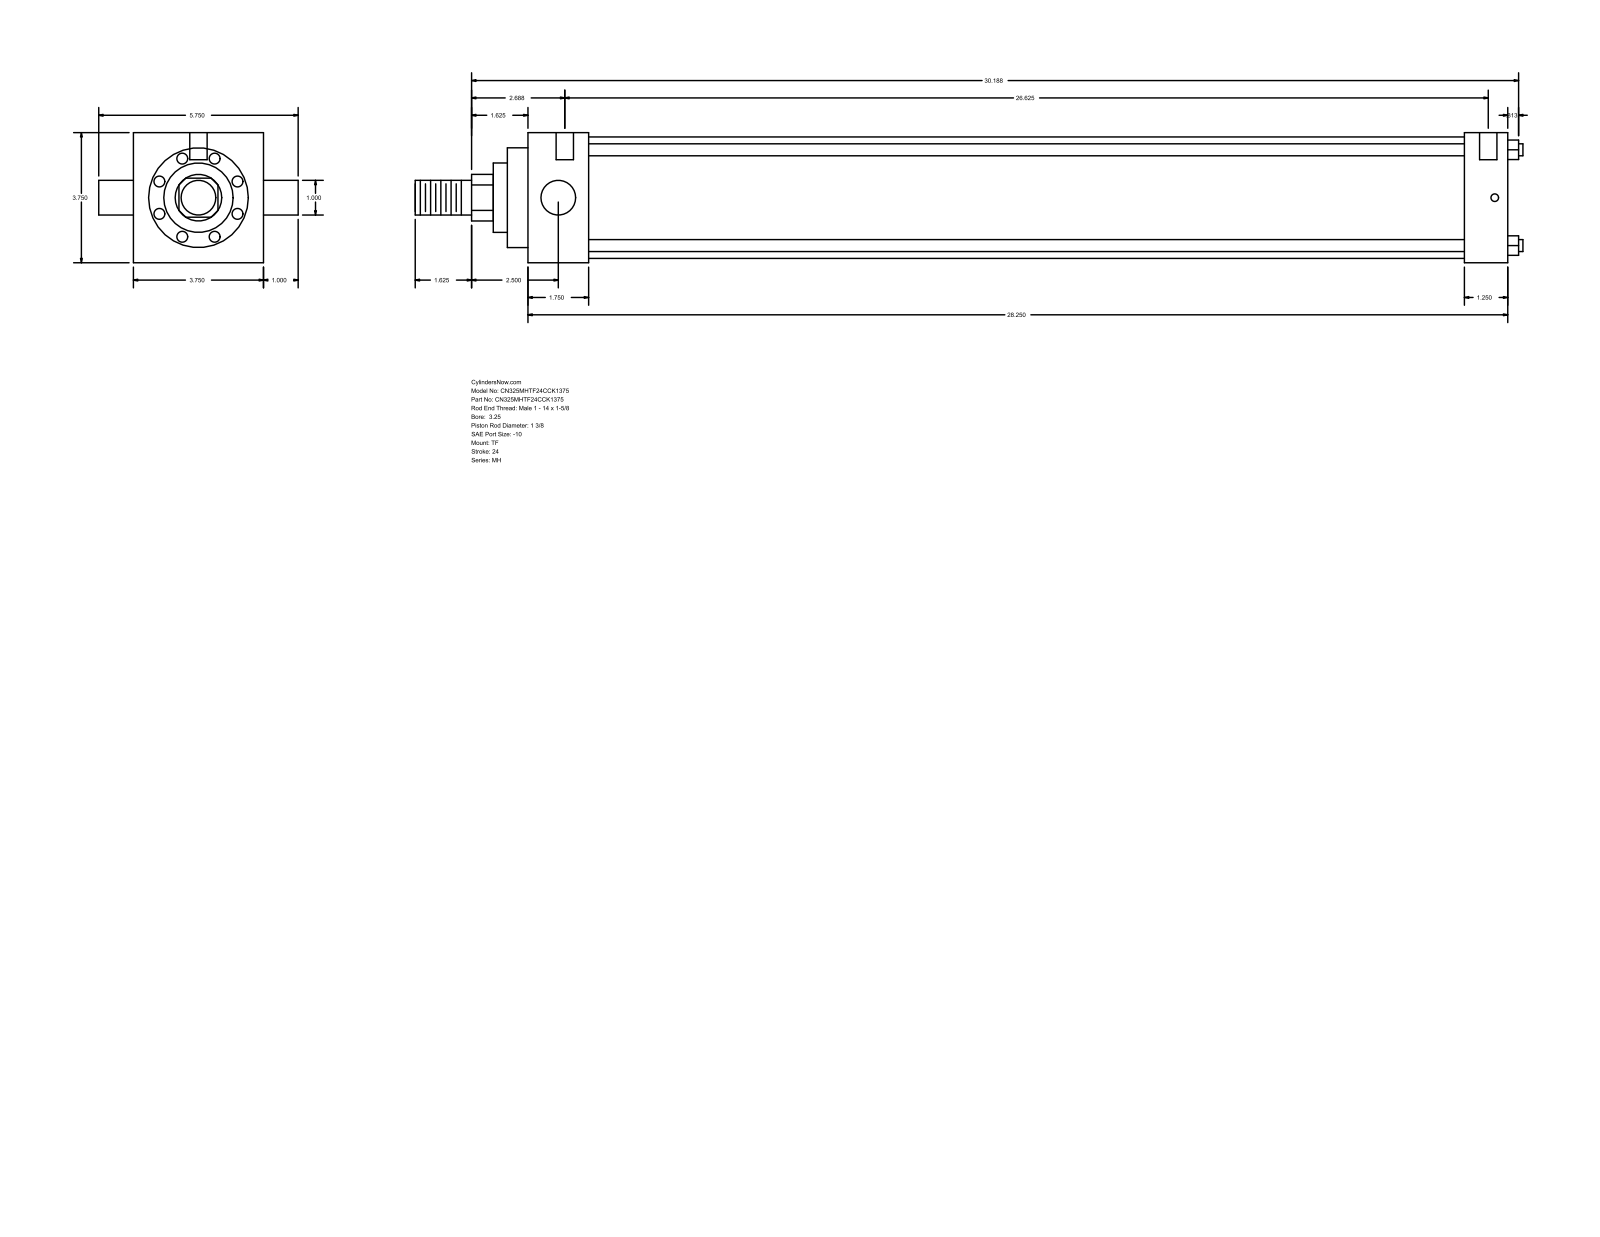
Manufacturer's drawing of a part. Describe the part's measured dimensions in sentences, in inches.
The part is named "MH_TF__0325_1.375". Its 3-D file was written by "GSSL Pune (CONFIG_CONTROL_DESIGN)". It is 0 solids with 86 faces: 61 planar, 25 cylindrical and 0 other. Overall it measures 31.937 by 5.75 by 3.75 inches. Round holes: 3 of diameter 0.219, 2 of diameter 0.5. Round bosses or shafts: 4 of diameter 0.345, 2 of diameter 1, 1 of diameter 3.5, 1 of diameter 2.875, 1 of diameter 2, 1 of diameter 1.375. Partial cylindrical surfaces (rounded edges, fillets, slot ends): 1 of radius 0.672. The main face-to-face distances are 3.75, 28.25, 1.75, 27, 25.25, 26.5, 1.25, 0.594, 2.344, 27.594. The hole center spacings are 0.063, 0.187, 26.625, 26.688, 26.813, 26.875.
